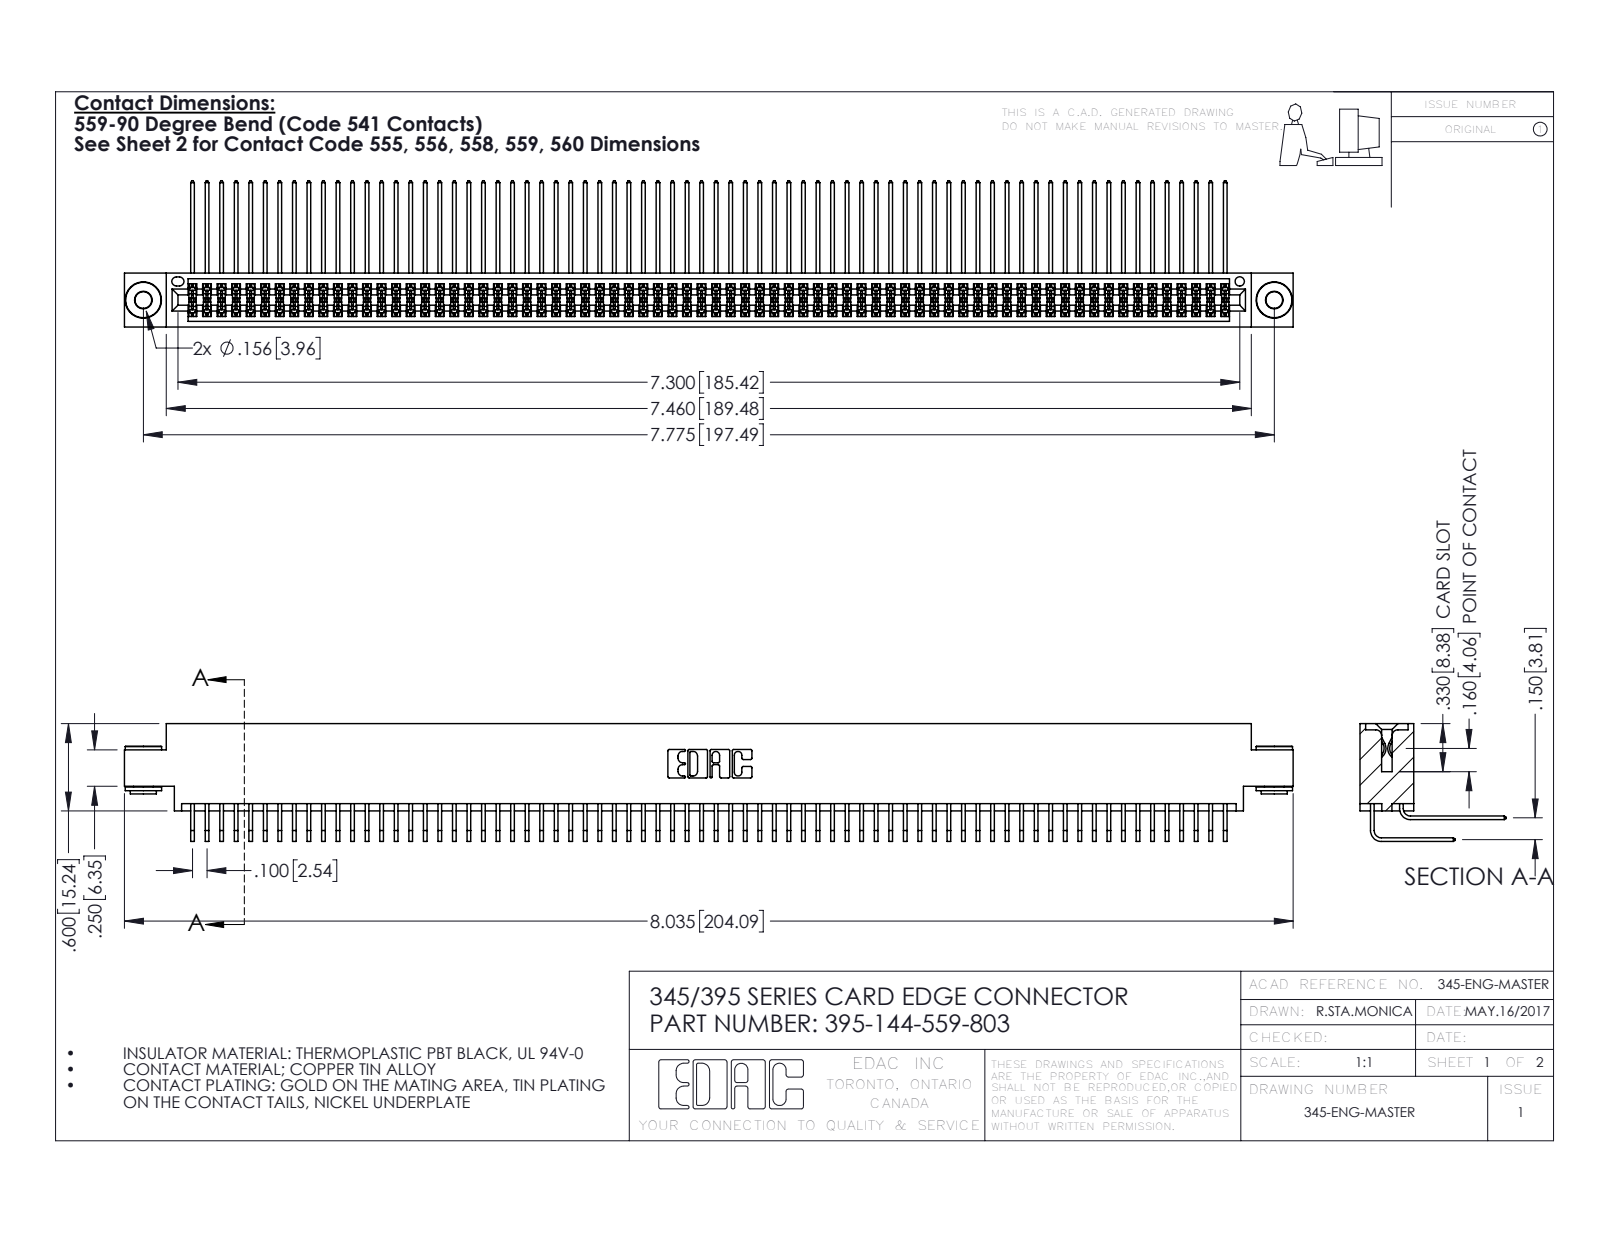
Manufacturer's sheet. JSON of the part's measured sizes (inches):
{"part_name": "345-250-002_345-250-002-102; 395-144-559-803; 345-292-001_559 Tail - 2; 345-292-001_558 559 Tail - 1 (+1 more)", "step_written_by": "SolidWorks 2016 (CONFIG_CONTROL_DESIGN)", "units": "inches", "bodies": {"solids": 147, "faces": 7656, "planar": 5134, "cylindrical": 2514, "other": 8}, "overall_size": [8.035, 1.005, 0.809], "volume_in3": 1.272, "surface_area_in2": 55.24, "round_holes": [[0.116, 2], [0.156, 2], [0.064, 1]], "round_bosses_or_shafts": [[0.25, 2], [0.18, 2], [0.136, 2]], "partial_cylinders_radius": [[0.006, 217], [0.01, 22], [0.007, 6], [0.031, 6], [0.026, 3], [0.014, 2], [0.019, 2], [0.022, 2]], "face_to_face_distances": [0.072, 0.298, 0.37, 0.2, 0.098, 0.272, 0.025, 0.225, 0.175, 0.15], "hole_center_spacings": [0.27, 7.539, 7.775]}
